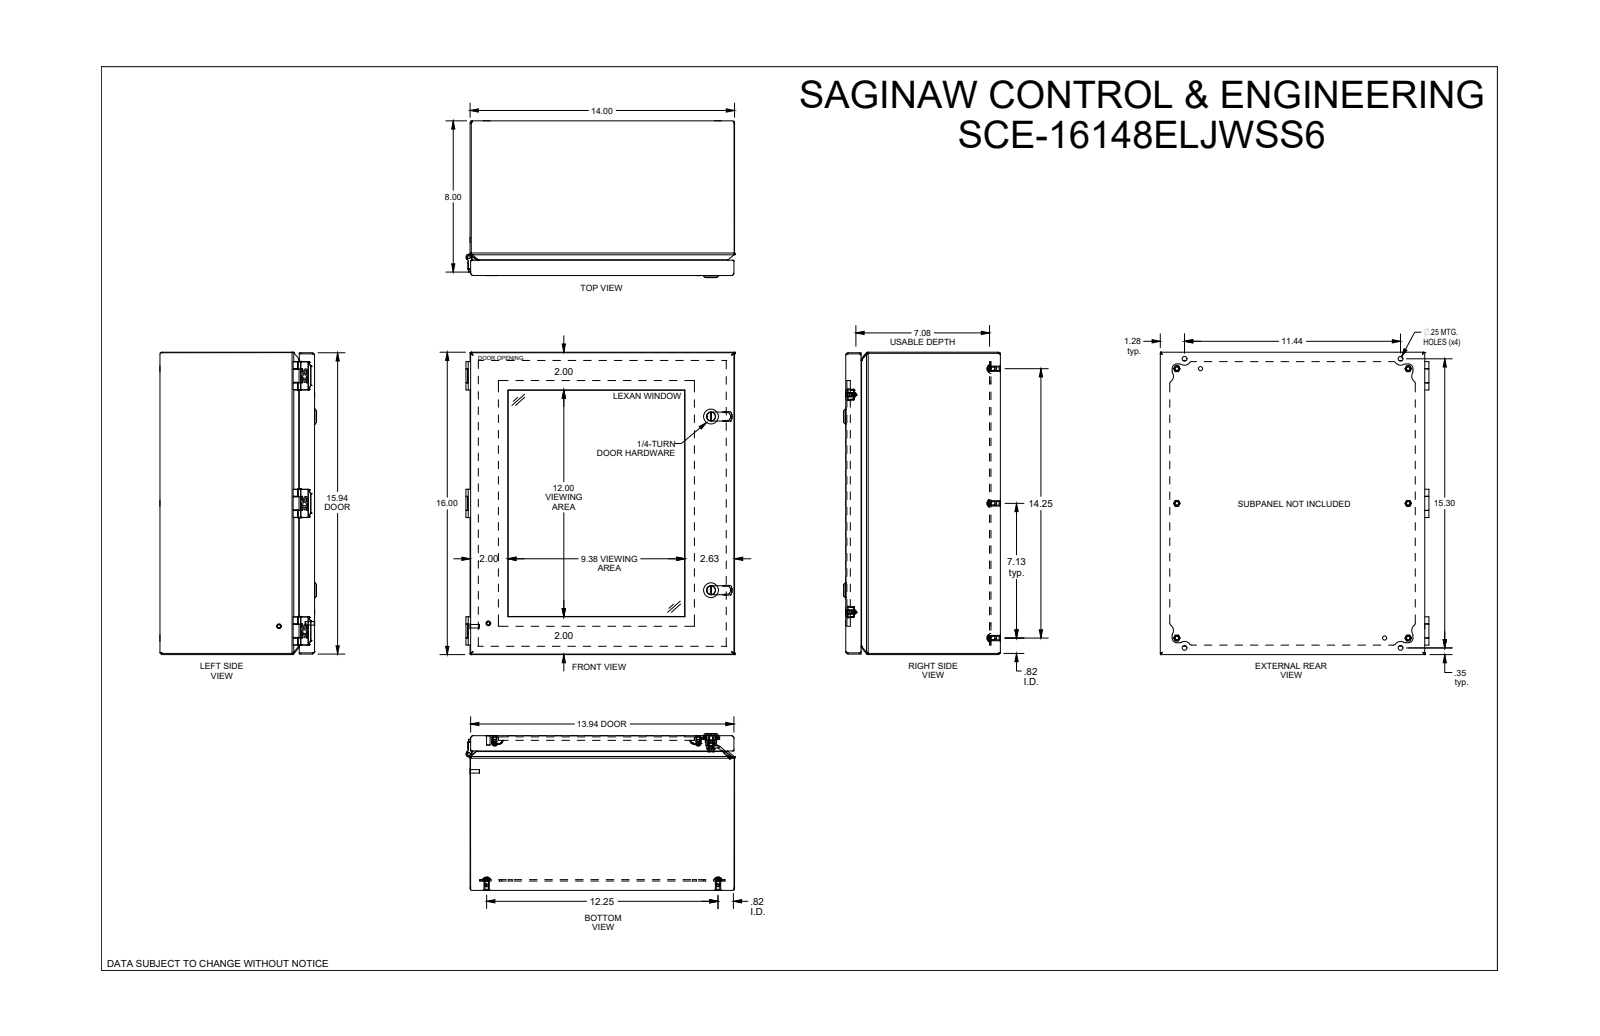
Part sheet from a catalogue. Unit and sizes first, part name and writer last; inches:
Units: inches
Overall size (bounding box): 16.06 × 14.22 × 8.296
Round holes (diameter × count): ⌀0.17 ×6, ⌀0.19 ×6, ⌀0.25 ×6, ⌀0.284 ×4, ⌀0.02 ×3, ⌀0.1 ×3, ⌀0.2 ×2, ⌀0.218 ×2, ⌀0.239 ×2, ⌀0.254 ×2, ⌀0.266 ×2, ⌀0.269 ×2
Round bosses / shafts (diameter × count): ⌀0.188 ×8, ⌀0.479 ×6, ⌀0.373 ×6, ⌀0.28 ×6, ⌀0.16 ×6, ⌀0.26 ×3, ⌀0.237 ×3, ⌀0.23 ×3
Partial cylindrical surfaces — rounded edges, fillets, slot ends (radius × count): R0.106 ×198, R0.005 ×114, R0.03 ×40, R0.025 ×36, R0.013 ×31, R0.01 ×18, R0.05 ×16, R0.25 ×13
Main face-to-face distances: 0.059, 14.001, 16.001, 0.571, 0.512, 0.496, 0.437, 0.075, 0.06, 7.944
Hole centre spacings: 6.75, 7.125, 14.171, 12.25, 13.5, 14.311, 0.06, 1.25
Volume: 101.6 in³ · Surface area: 2 512 in²
Bodies: 52 solids, 2925 faces (811 planar, 819 cylindrical, 1295 other)
Part name (STEP PRODUCT): SCE-16148ELJW
STEP written by: SolidWorks 2019 (AUTOMOTIVE_DESIGN)
